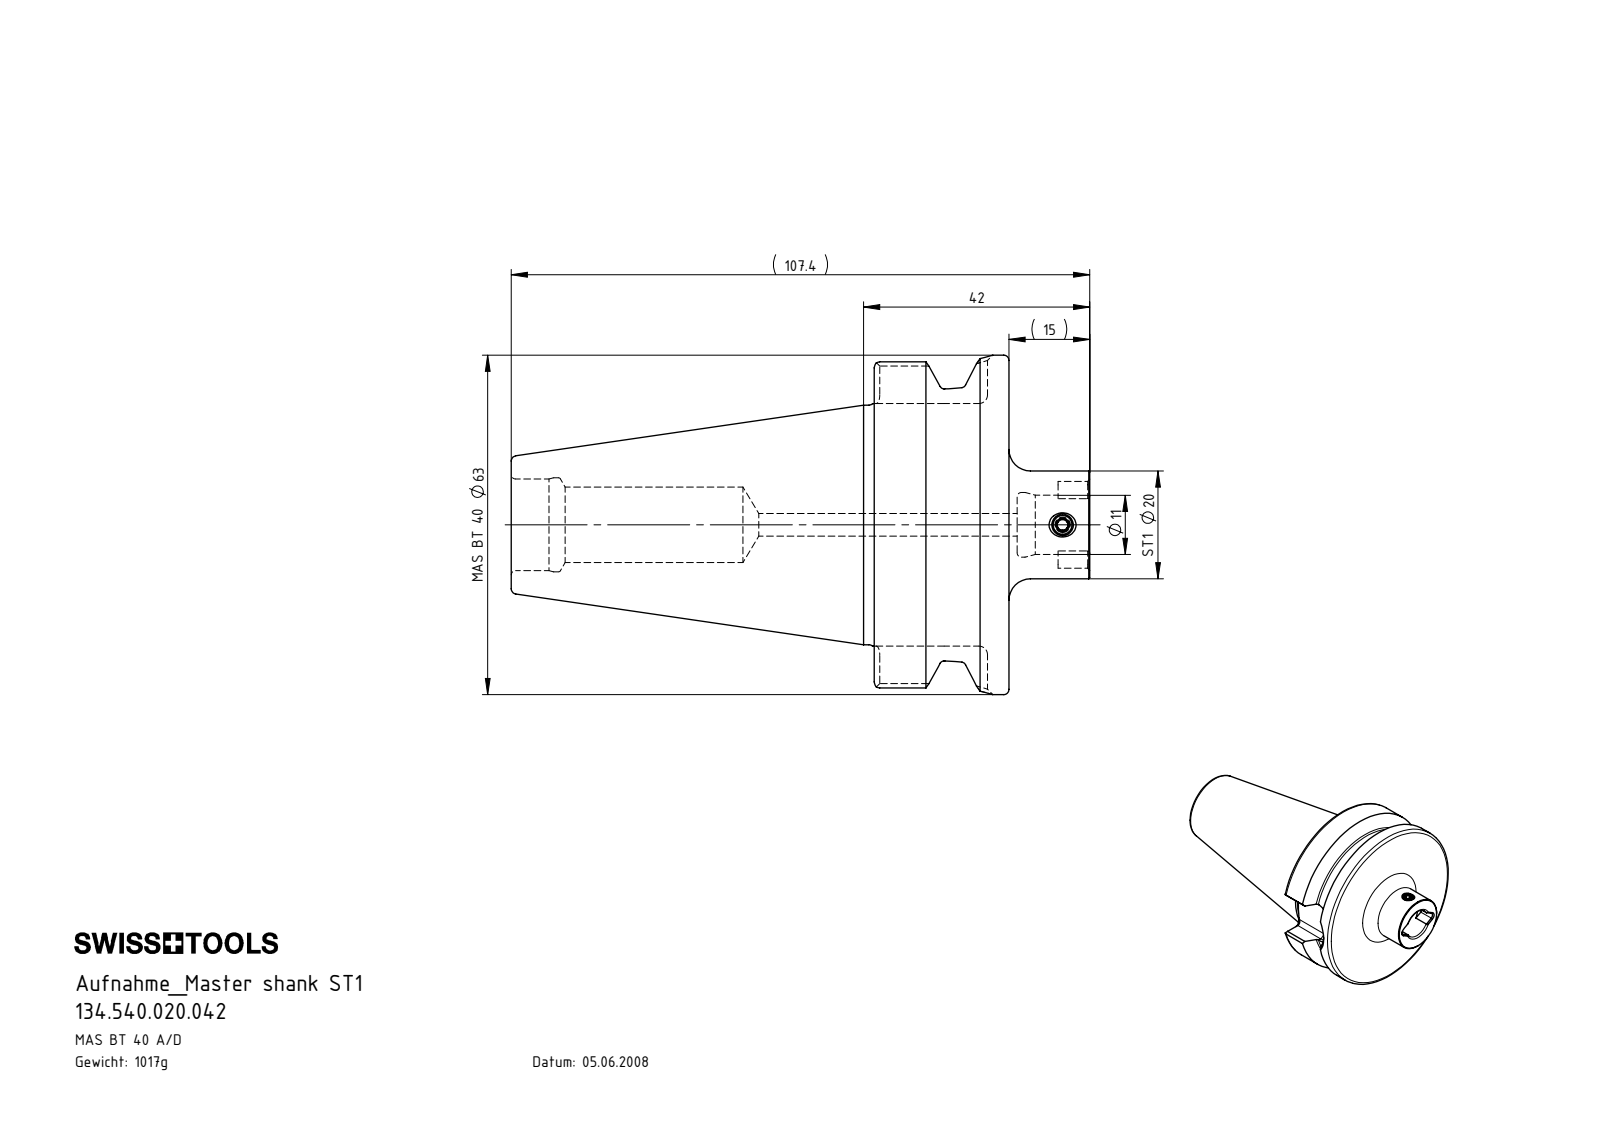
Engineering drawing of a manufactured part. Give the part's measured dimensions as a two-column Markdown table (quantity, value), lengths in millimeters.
| quantity | value |
| --- | --- |
| part name | BT4-ST1.K01.042; ST1-ER1.001.005_A; BT4-ST1.K01.042_B |
| STEP written by | SolidWorks 2017 (CONFIG_CONTROL_DESIGN) |
| units | millimeters |
| bodies | 2 solids, 146 faces (42 planar, 42 cylindrical, 62 other) |
| overall size | 107.4 × 63 × 63 |
| volume | 129 574 mm³ |
| surface area | 22 368 mm² |
| round holes (diameter × count) | 2 × 1, 3.5 × 1, 4.2 × 1, 11 × 1, 12 × 1, 14 × 1, 17 × 1, 17.45 × 1 |
| round bosses / shafts (diameter × count) | 63 × 1, 53 × 1, 44.45 × 1, 20 × 1, 4 × 1 |
| partial cylindrical surfaces (radius × count) | 1.6 × 8, 1.3 × 2, 8.05 × 1 |
| main face-to-face distances | 25, 45, 40, 15, 67.4, 92.4, 107.4, 16.1, 93.9, 26.5 |
